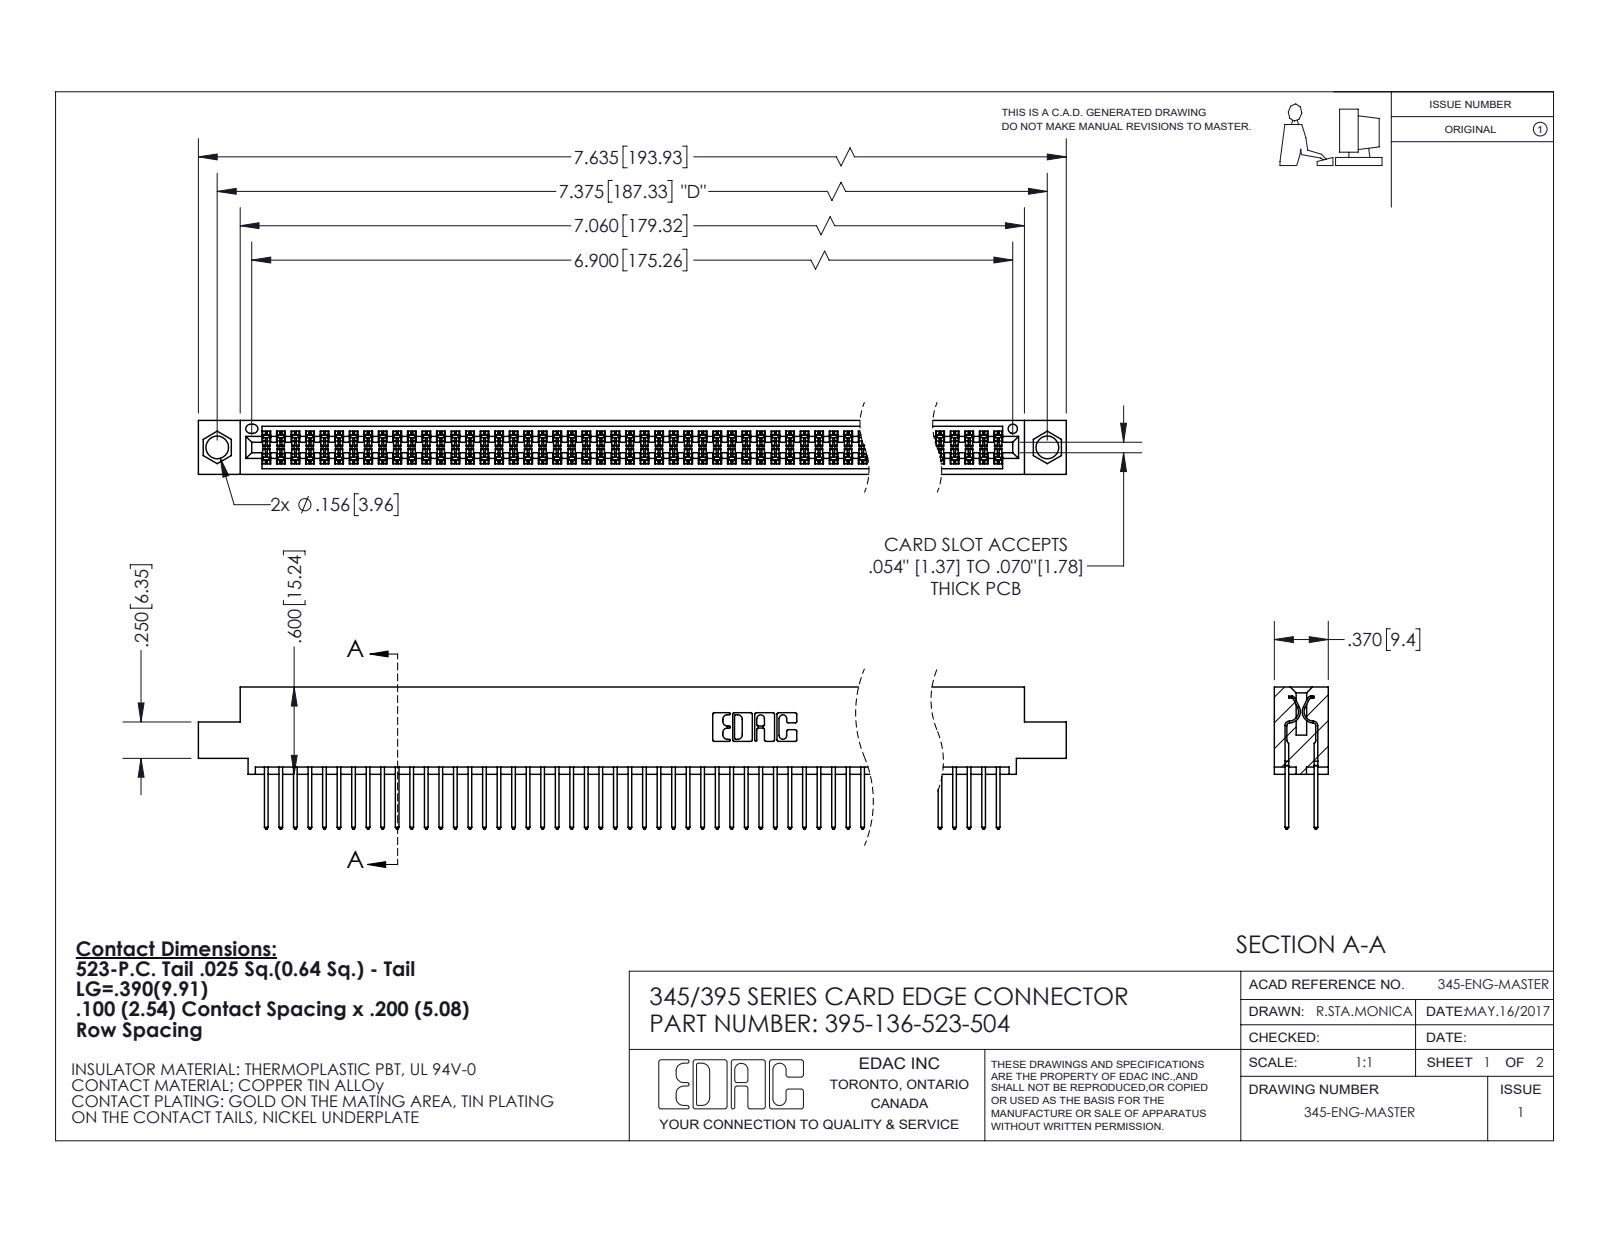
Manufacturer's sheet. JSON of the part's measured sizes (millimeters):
{"part_name": "395-136-523-504; 345-292-001_345-293-123; 345 Part_0.110 Offset - 0.156 Dia-TI", "step_written_by": "SolidWorks 2020 (CONFIG_CONTROL_DESIGN)", "units": "millimeters", "bodies": {"solids": 137, "faces": 6944, "planar": 4586, "cylindrical": 2358, "other": 0}, "overall_size": [193.9, 24.8, 9.4], "volume_mm3": 19170, "surface_area_mm2": 30050, "round_holes": [[4, 2], [1.6, 1]], "partial_cylinders_radius": [[0.2, 204], [0.3, 136], [0.3, 22], [0.2, 6], [0.8, 6], [0.7, 3], [0.4, 2], [0.5, 2]], "face_to_face_distances": [1.8, 7.6, 5.1, 2.5, 6.9, 0.6, 9.4, 5.7, 4.4, 3.8], "hole_center_spacings": [6.9, 181.3, 187.3]}
